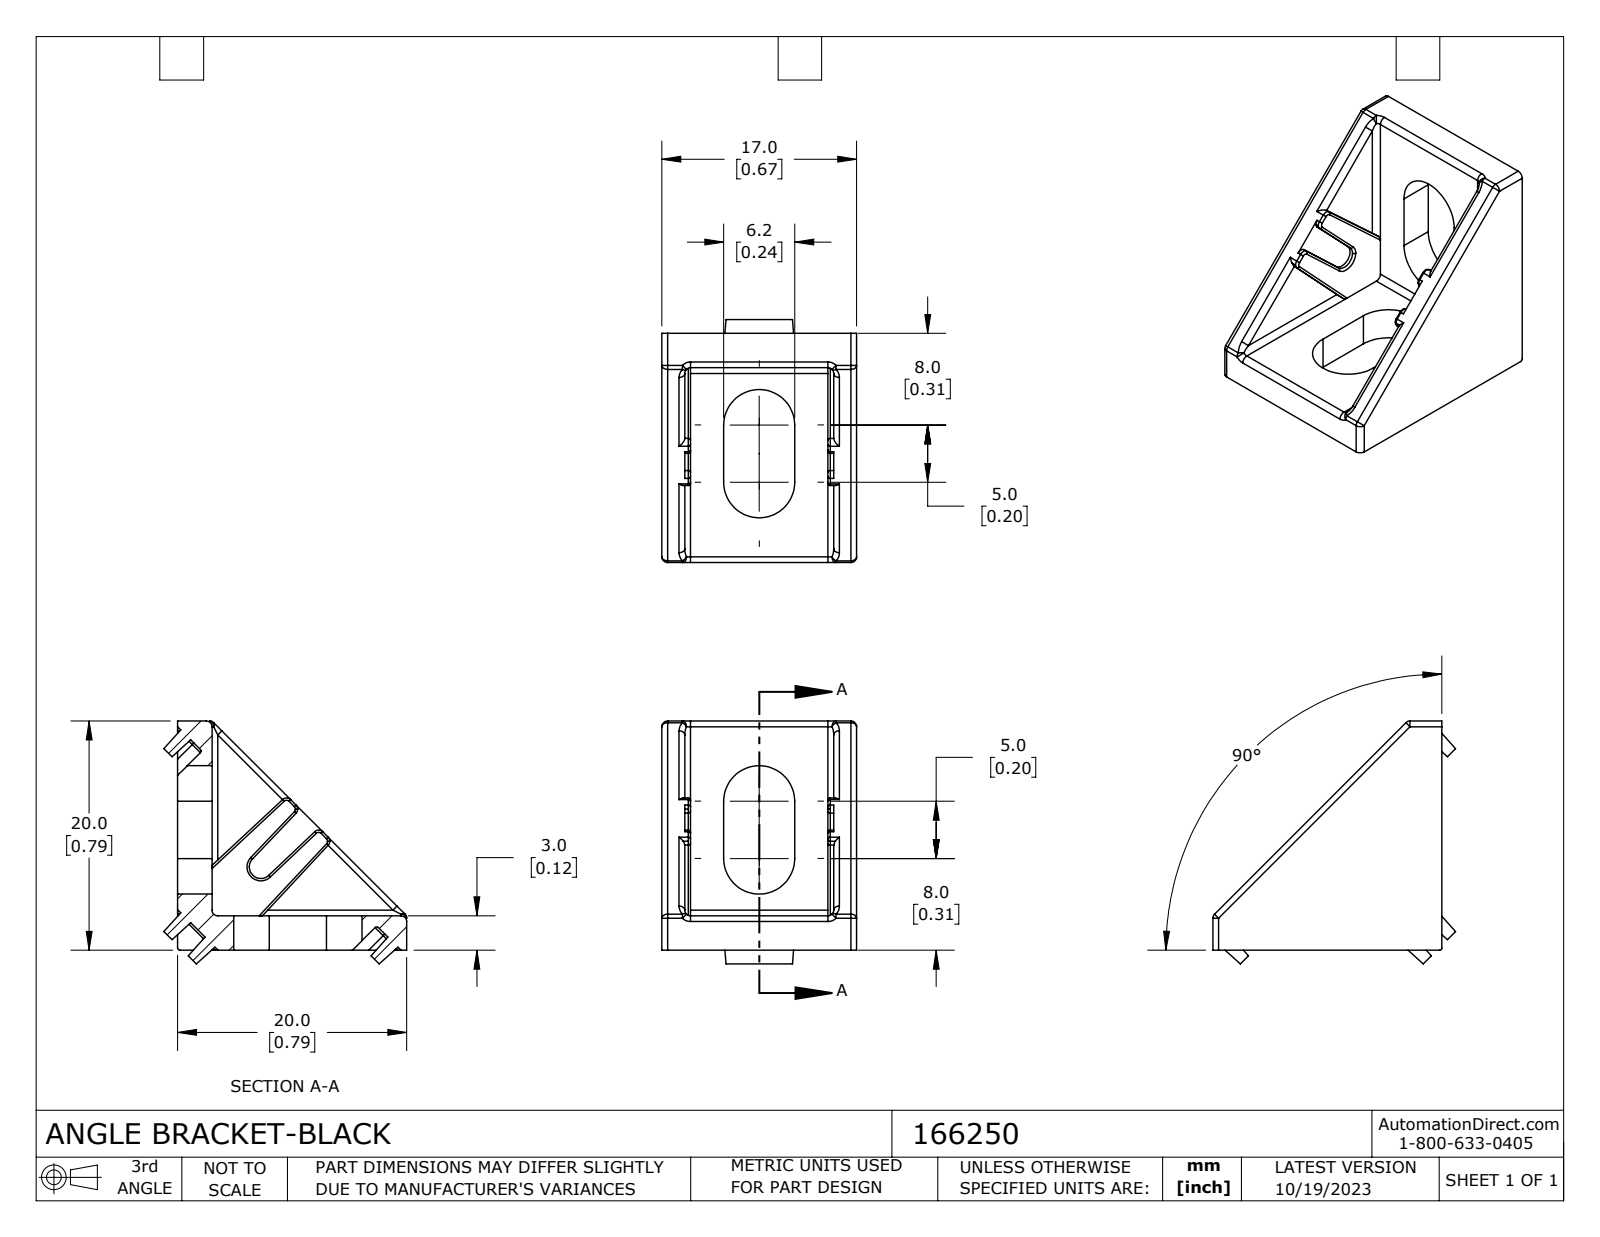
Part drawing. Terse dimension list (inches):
name: 166250
written by: SolidWorks 2023 (CONFIG_CONTROL_DESIGN)
unit: in
bodies: 1 solid, 160 faces (61 planar, 66 cylindrical, 33 other)
size: 0.835 × 0.835 × 0.669
volume: 0.122 in³; area: 3.385 in²
rounds: 21× R0.02, 17× R0.008, 4× R0.039, 4× R0.122, 1× R0.039
face distances: 0.669, 0.118, 0.079, 0.591, 0.787, 0.098, 0.571, 0.02, 0.492, 0.512
